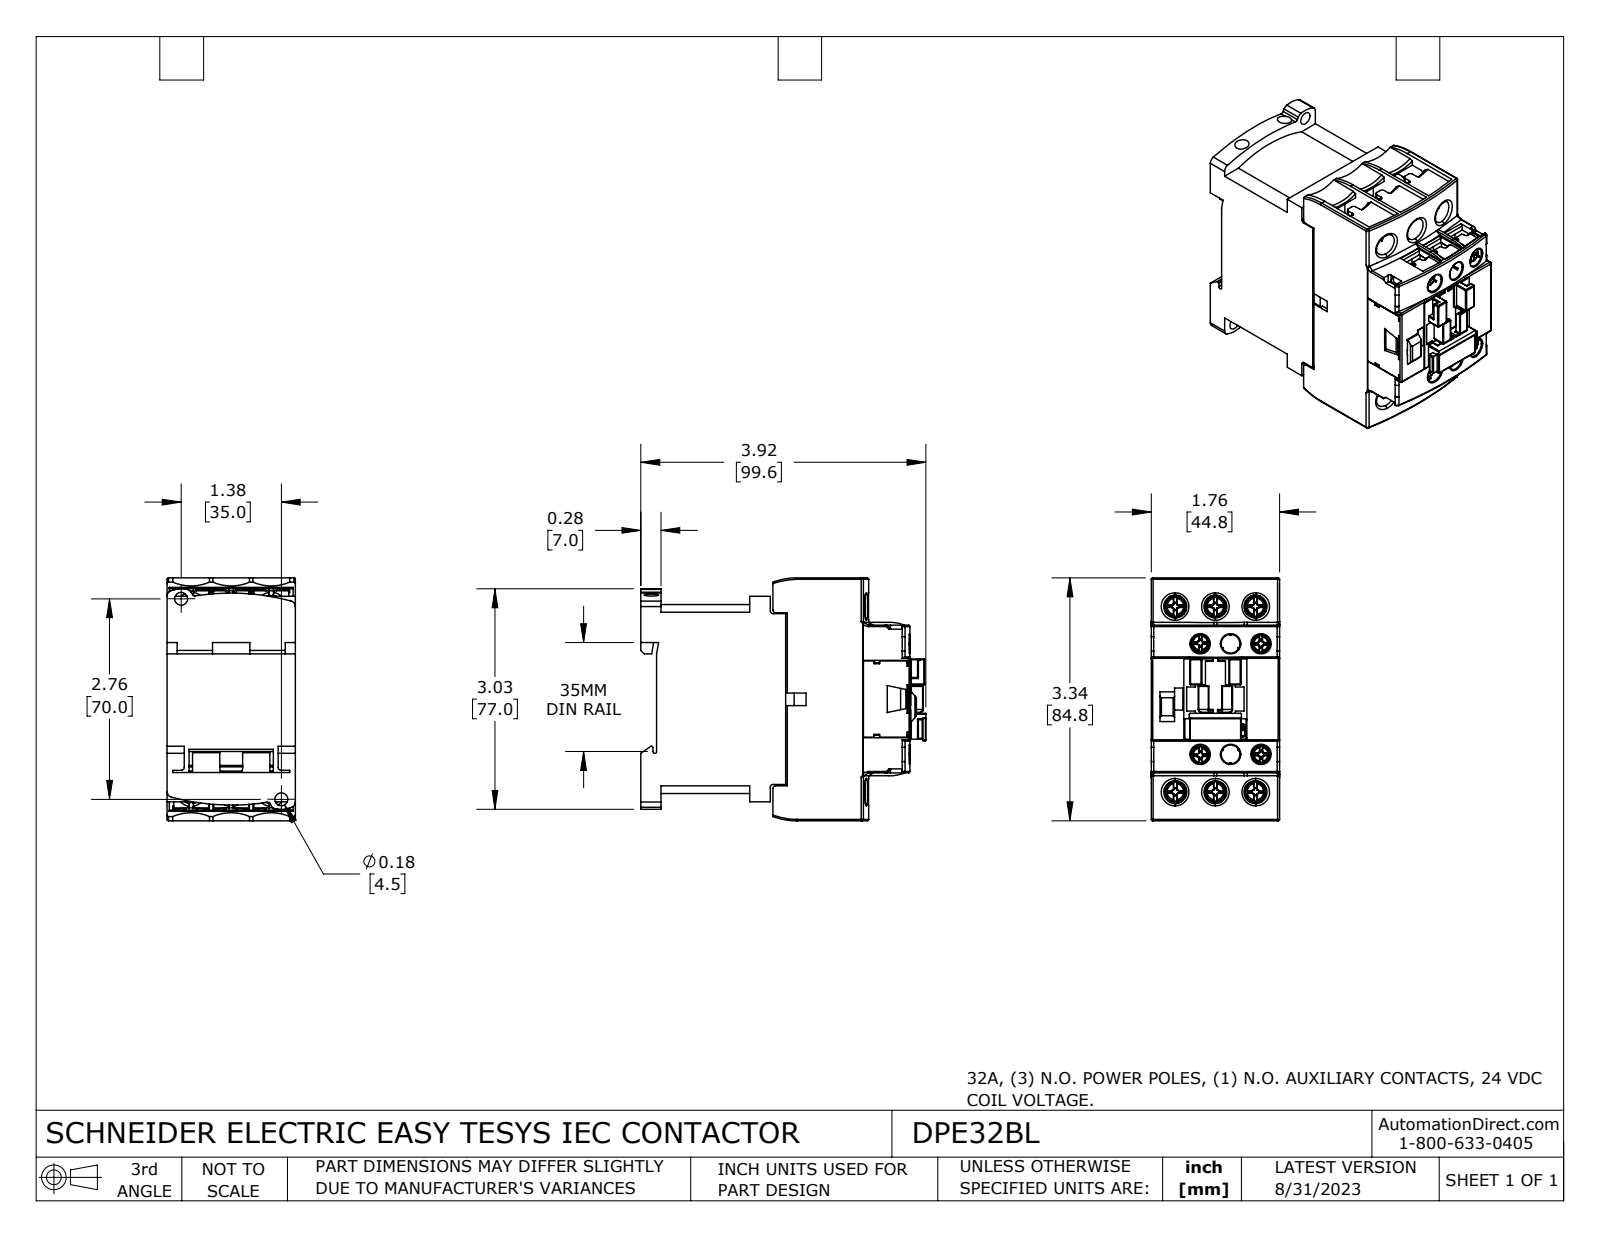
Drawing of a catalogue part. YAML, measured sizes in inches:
part_name: "DPE32BL"
step_written_by: "SolidWorks 2021 (CONFIG_CONTROL_DESIGN)"
units: inches
bodies: {solids: 14, faces: 2629, planar: 1674, cylindrical: 587, other: 368}
overall_size: [3.919, 3.339, 1.764]
volume: 15.47
surface_area: 104.1
round_holes:
  - {diameter: 0.256, count: 6}
  - {diameter: 0.315, count: 6}
  - {diameter: 0.039, count: 2}
  - {diameter: 0.177, count: 2}
  - {diameter: 0.197, count: 2}
round_bosses_or_shafts:
  - {diameter: 0.157, count: 8}
  - {diameter: 0.126, count: 6}
  - {diameter: 0.138, count: 4}
  - {diameter: 0.134, count: 4}
  - {diameter: 0.108, count: 4}
  - {diameter: 0.394, count: 3}
  - {diameter: 0.02, count: 1}
partial_cylinders:
  - {radius: 0.012, count: 51}
  - {radius: 0.02, count: 39}
  - {radius: 0.006, count: 36}
  - {radius: 0.039, count: 30}
  - {radius: 0.63, count: 18}
  - {radius: 0.008, count: 15}
  - {radius: 0.031, count: 10}
  - {radius: 0.079, count: 10}
face_to_face_distances: [1.764, 1.043, 0.551, 0.096, 0.947, 0.031, 0.047, 0.059, 1.892, 1.795]
hole_center_spacings: [0.417, 0.551, 1.576, 2.61, 1.52, 2.551, 0.553, 0.56]
